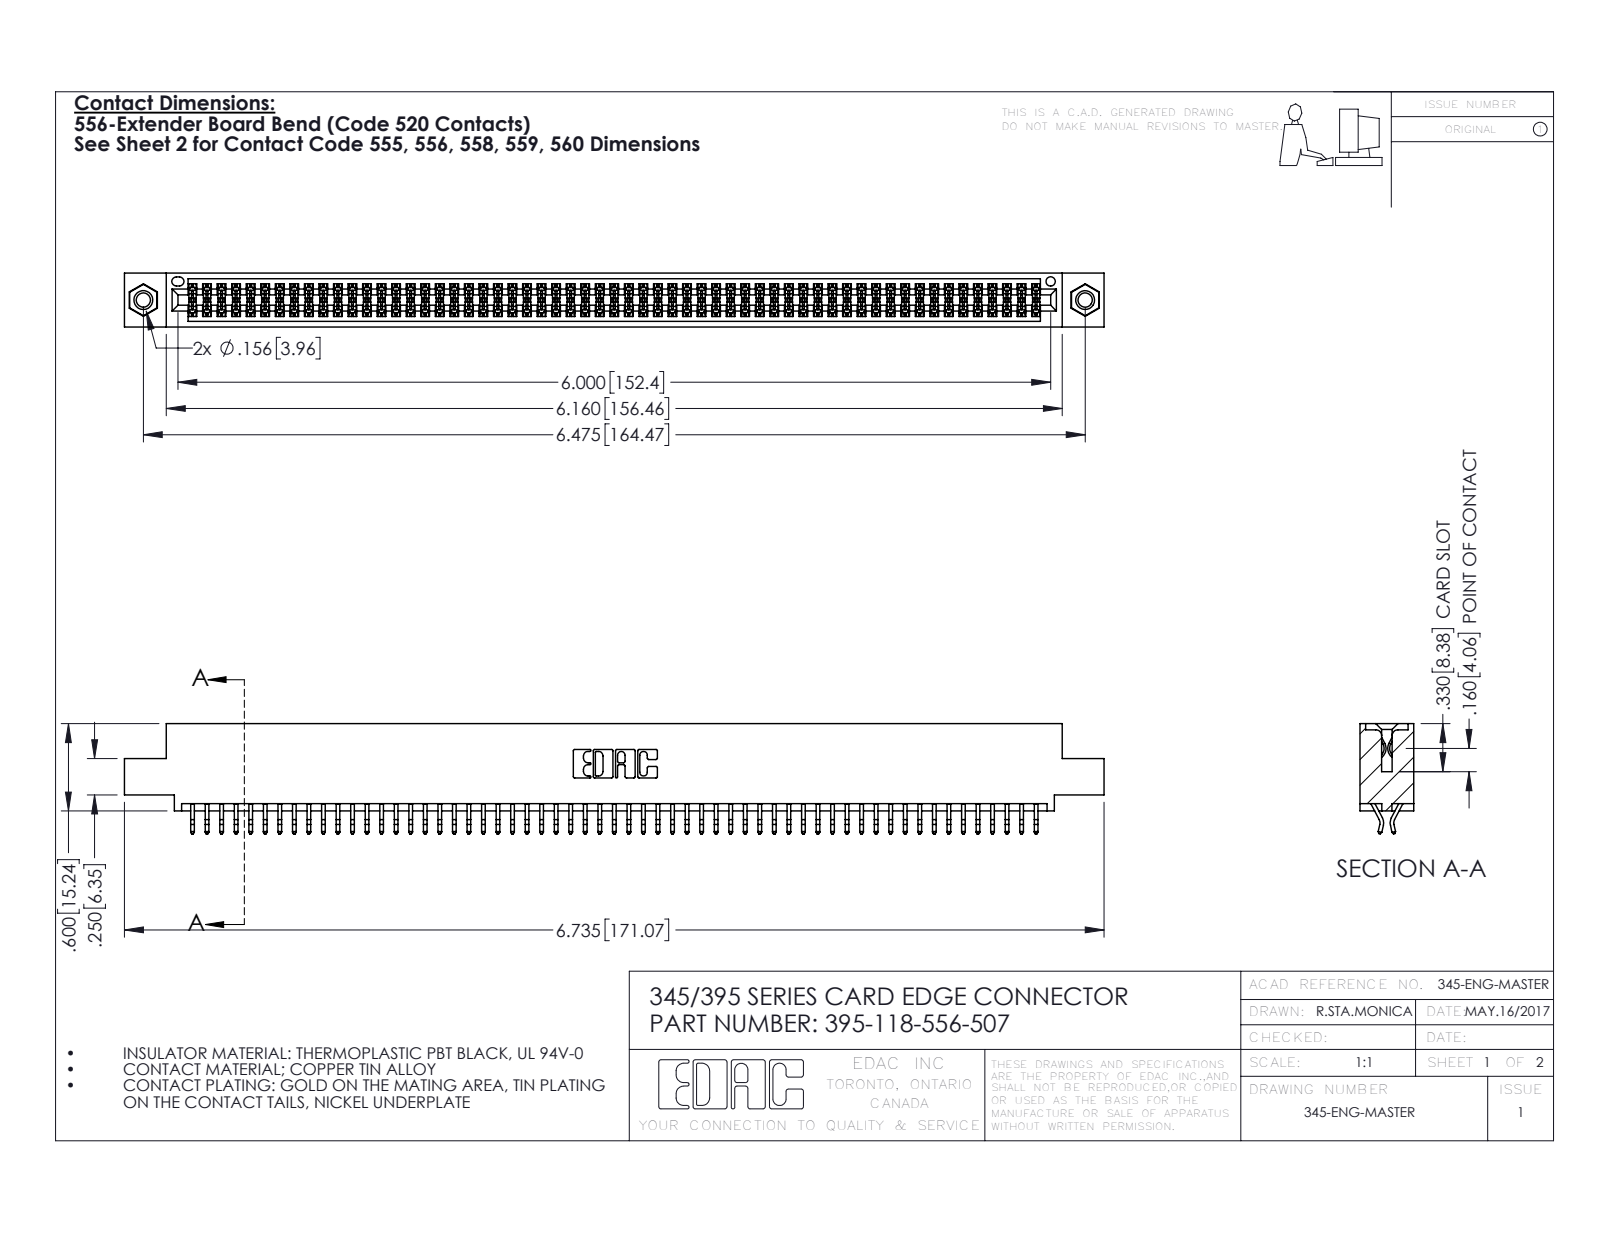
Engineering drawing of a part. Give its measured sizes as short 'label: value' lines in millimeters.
name: 345 Part_0.110 Offset - 0.156 Dia-TI; 395-118-556-507; 345-292-001_556 Tail; 345-250-001_345-250-005-103
written by: SolidWorks 2016 (CONFIG_CONTROL_DESIGN)
unit: mm
bodies: 121 solids, 6798 faces (4482 planar, 2300 cylindrical, 16 other)
size: 171.1 × 19.2 × 9.4
volume: 16 680 mm³; area: 25 010 mm²
holes: 2× ⌀2.5, 2× ⌀3.2, 2× ⌀4, 1× ⌀1.6
bosses: 2× ⌀3.9
rounds: 177× R0.2, 22× R0.3, 6× R0.2, 6× R0.8, 3× R0.7, 2× R0.3, 2× R0.4, 2× R0.5
face distances: 1.8, 7.6, 9.4, 5.1, 0.6, 2.5, 6.9, 5.7, 4.4, 3.8
hole spacings: 6.9, 158.5, 164.5
